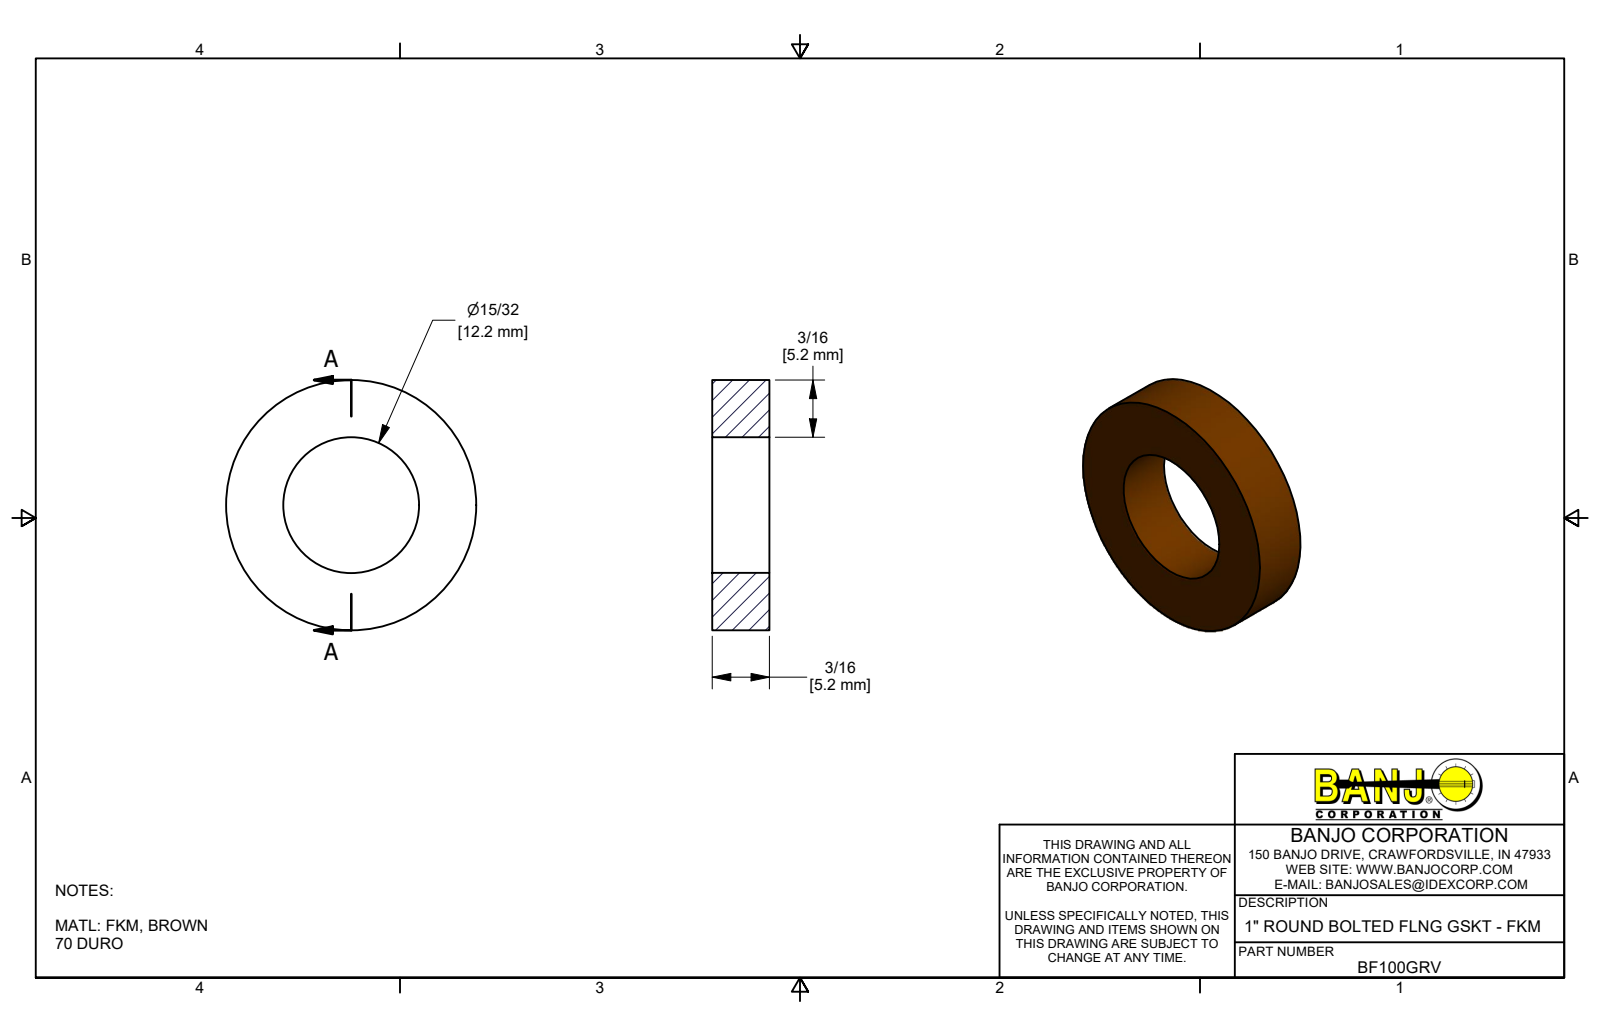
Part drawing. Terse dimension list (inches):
name: BF100GRV
written by: Autodesk Inventor 2019 (AUTOMOTIVE_DESIGN)
unit: in
bodies: 1 solid, 4 faces (2 planar, 2 cylindrical, 0 other)
size: 0.886 × 0.886 × 0.203
volume: 0.088 in³; area: 1.742 in²
holes: 1× ⌀0.48
bosses: 1× ⌀0.886
face distances: 0.203
